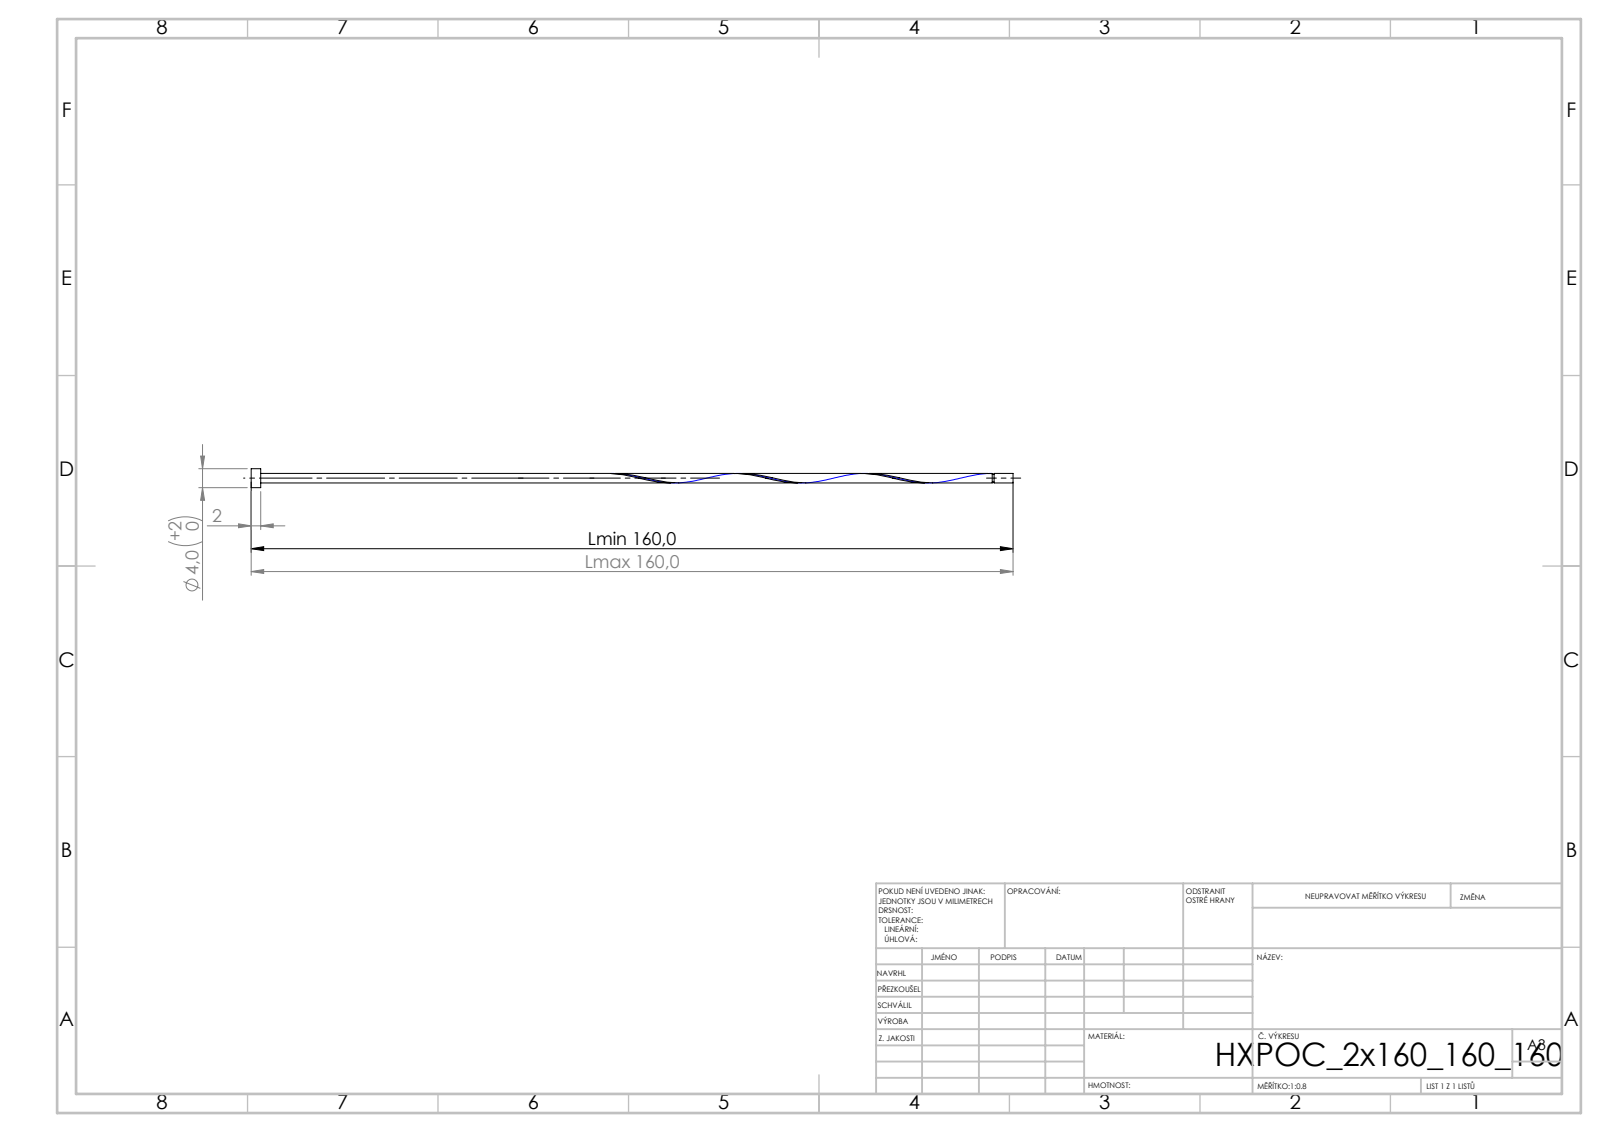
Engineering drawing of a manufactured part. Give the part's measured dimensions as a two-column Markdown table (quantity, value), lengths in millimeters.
| quantity | value |
| --- | --- |
| STEP written by | SolidWorks 2019 (CONFIG_CONTROL_DESIGN) |
| units | millimeters |
| bodies | 1 solid, 16 faces (6 planar, 9 cylindrical, 1 other) |
| overall size | 160 × 4 × 4 |
| volume | 628 mm³ |
| surface area | 1 395 mm² |
| round bosses / shafts (diameter × count) | 4 × 1, 2 × 1, 1.6 × 1 |
| main face-to-face distances | 2, 160, 158, 156.02, 154.02, 3.98, 155.62, 153.62, 0.4, 4.38 |
